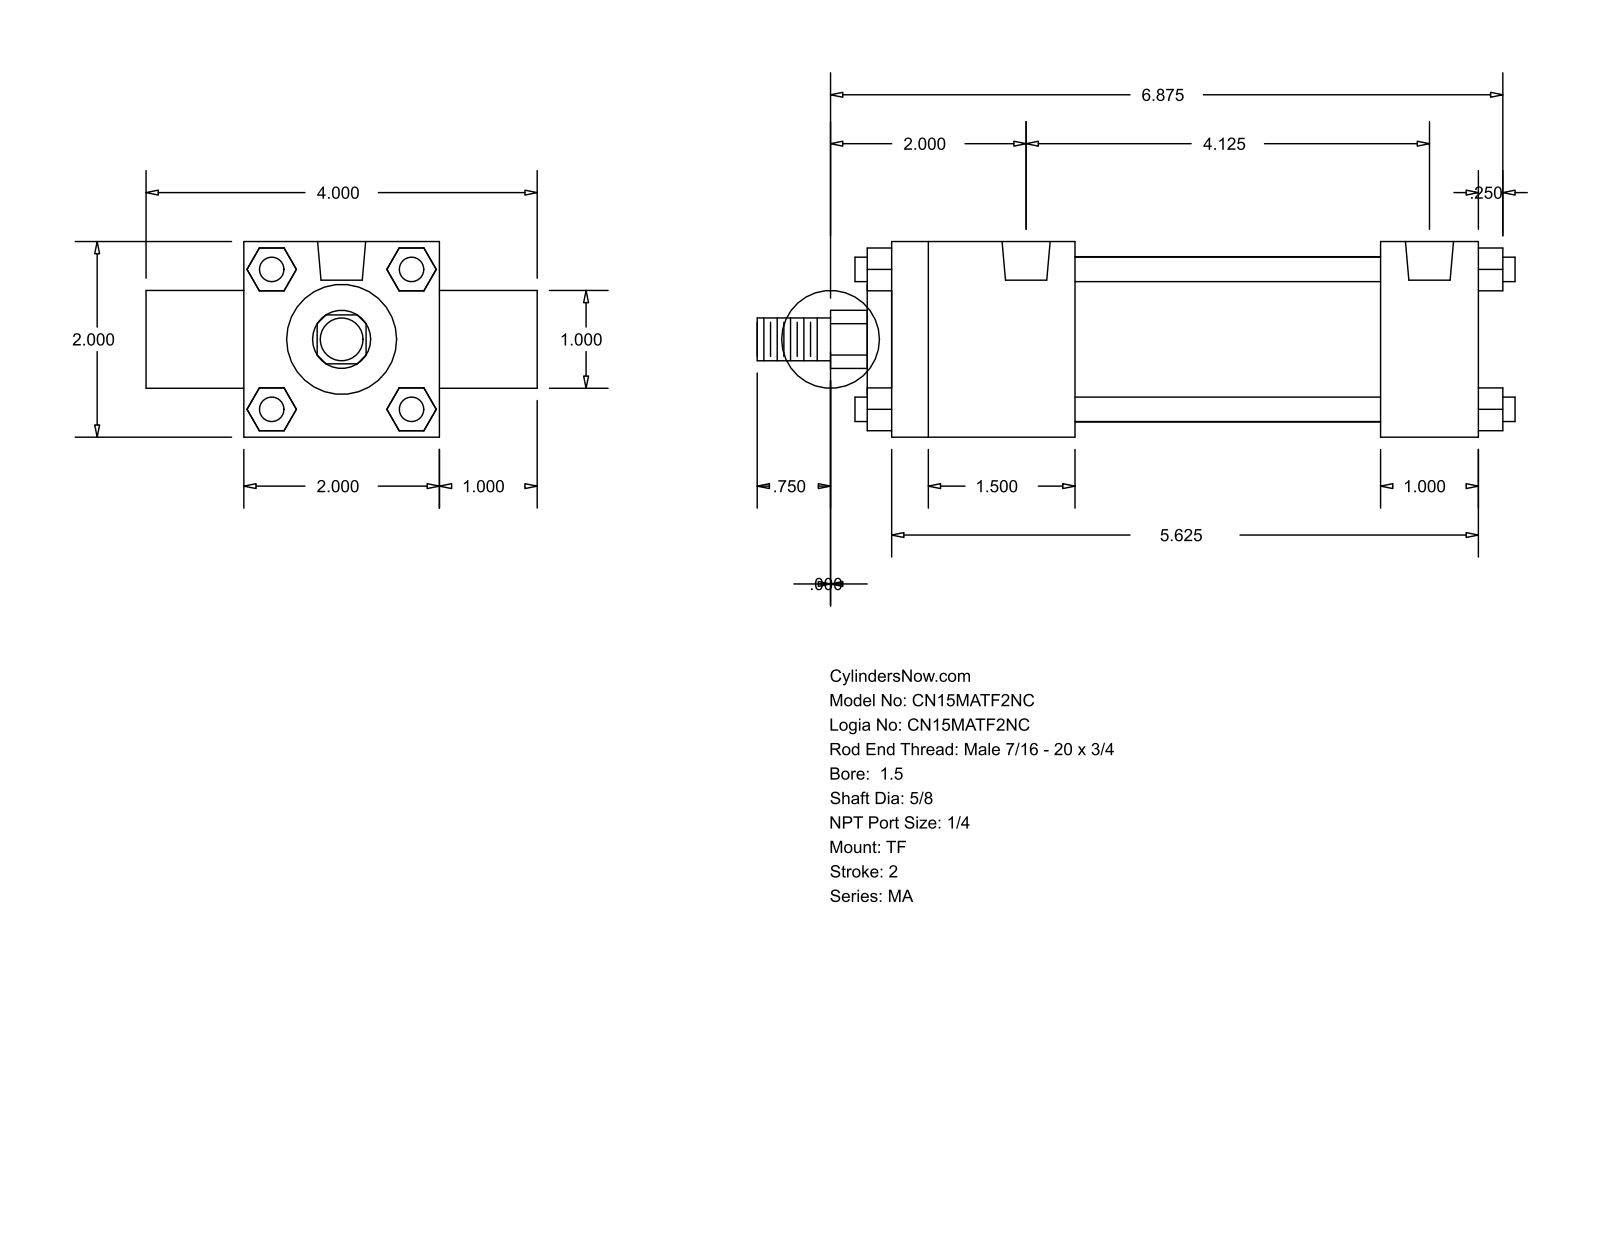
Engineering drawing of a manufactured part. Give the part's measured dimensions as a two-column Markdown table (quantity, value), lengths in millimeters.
| quantity | value |
| --- | --- |
| part name | MA_TF__0150_0.625 |
| STEP written by | GSSL Pune (CONFIG_CONTROL_DESIGN) |
| units | millimeters |
| bodies | 0 solids, 120 faces (92 planar, 28 cylindrical, 0 other) |
| overall size | 196.85 × 101.6 × 50.8 |
| round holes (diameter × count) | 7.94 × 3, 12.49 × 2 |
| round bosses / shafts (diameter × count) | 6.35 × 4, 42.93 × 1, 28.57 × 1, 25.4 × 1, 15.88 × 1, 11.11 × 1 |
| partial cylindrical surfaces (radius × count) | 7.54 × 1 |
| main face-to-face distances | 50.8, 25.4, 152.4, 76.2, 47.62, 127, 79.38, 104.78, 6.35, 53.97 |
| hole center spacings | 104.77 |
